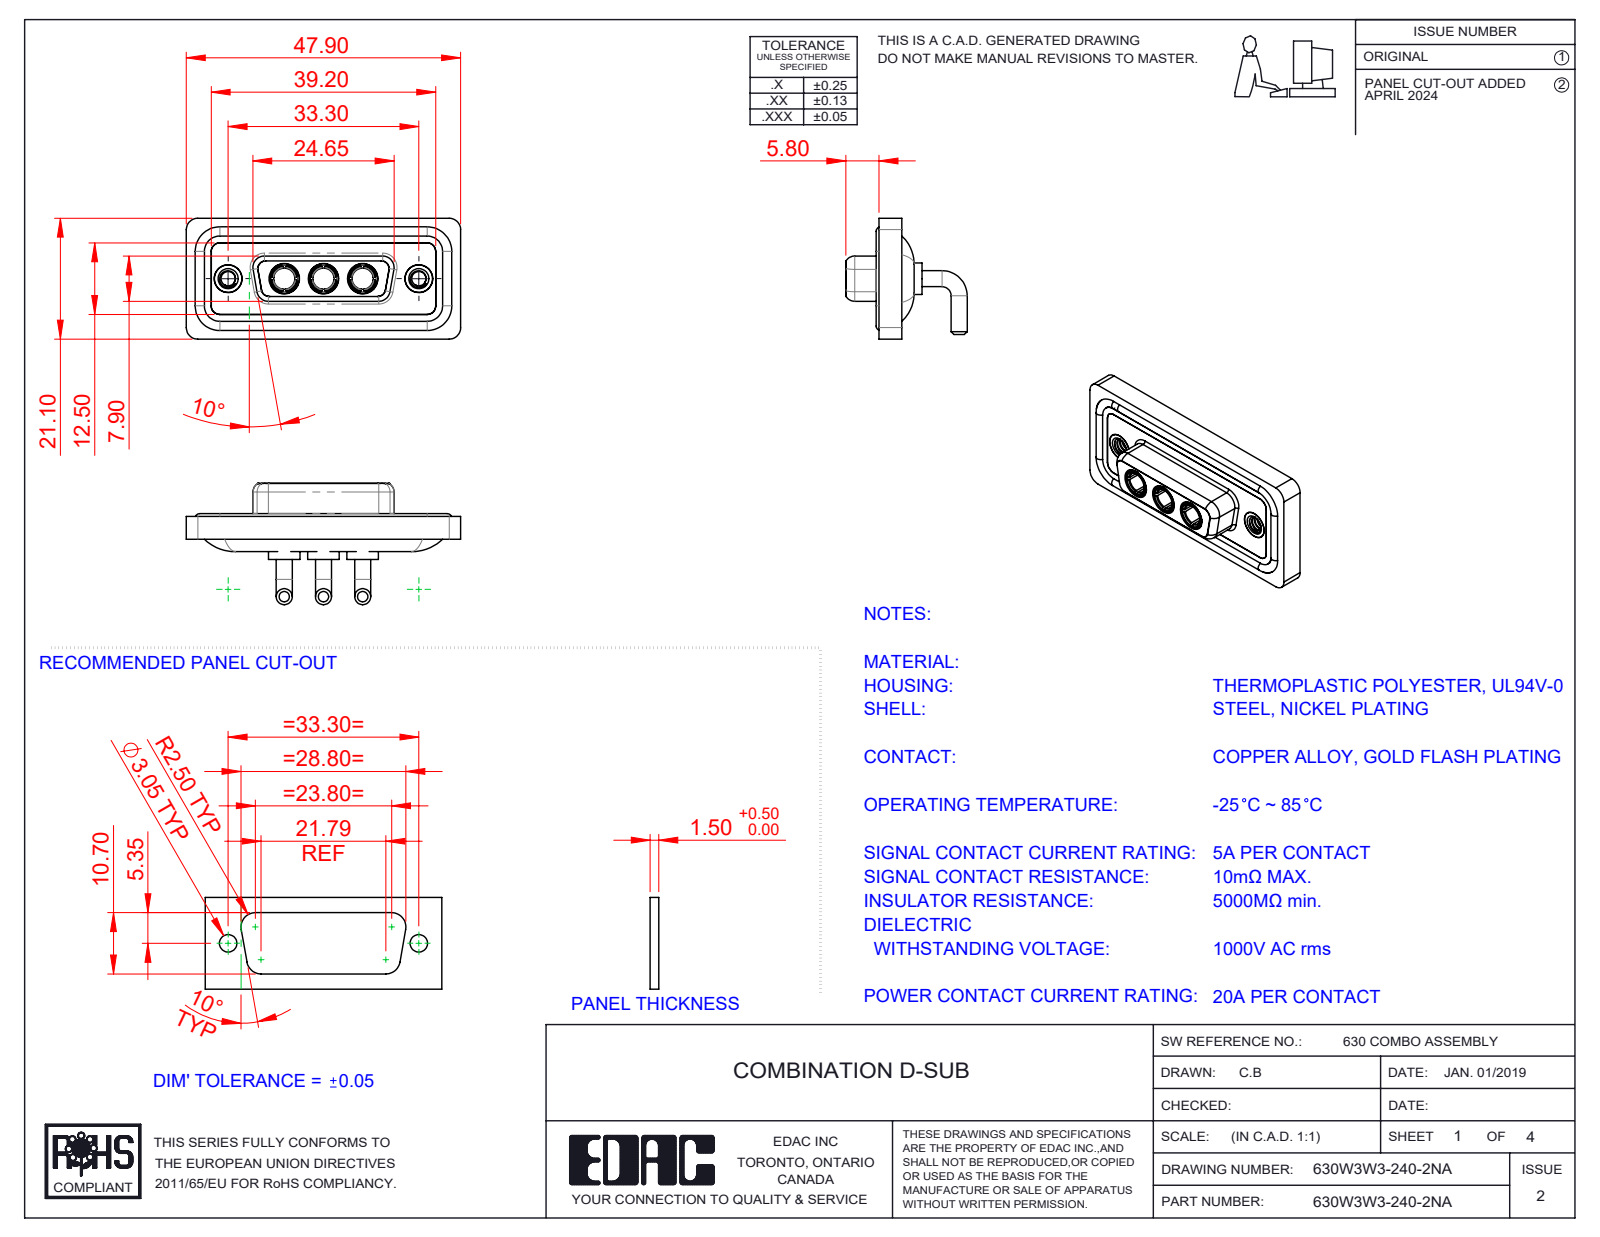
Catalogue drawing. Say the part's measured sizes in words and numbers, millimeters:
The part is named "630Combo Threaded Rivet_A; Power Socket_20A RA; 630Combo Housing_3W3; 630W3W3-140-2NA (+3 more)". Its 3-D file was written by "SolidWorks 2023 (CONFIG_CONTROL_DESIGN)". It is 13 solids with 614 faces: 192 planar, 261 cylindrical and 161 other. Overall it measures 47.9 by 21.2 by 21.1 millimeters. Its volume is 6 172 cubic millimeters and its surface area 9 975 square millimeters. Round holes: 5 of diameter 4.85, 3 of diameter 3.7, 3 of diameter 5.3, 2 of diameter 2.5, 2 of diameter 4, 2 of diameter 4.05, 2 of diameter 5. Round bosses or shafts: 6 of diameter 2.8, 4 of diameter 1.6, 3 of diameter 5.5, 3 of diameter 5.2, 3 of diameter 4.96, 3 of diameter 4.75, 3 of diameter 3.75, 2 of diameter 4.95. Partial cylindrical surfaces (rounded edges, fillets, slot ends): 20 of radius 2, 18 of radius 1.5, 12 of radius 1.35, 8 of radius 1.6, 4 of radius 0.25, 4 of radius 0.5, 4 of radius 0.6, 4 of radius 0.65. The main face-to-face distances are 0.4, 1.8, 1.1, 1.6, 2.9, 2.5, 3.1, 3.7, 4.1, 1.5. The hole center spacings are 6.85, 9.8, 16.65, 23.5, 13.7, 33.3.
